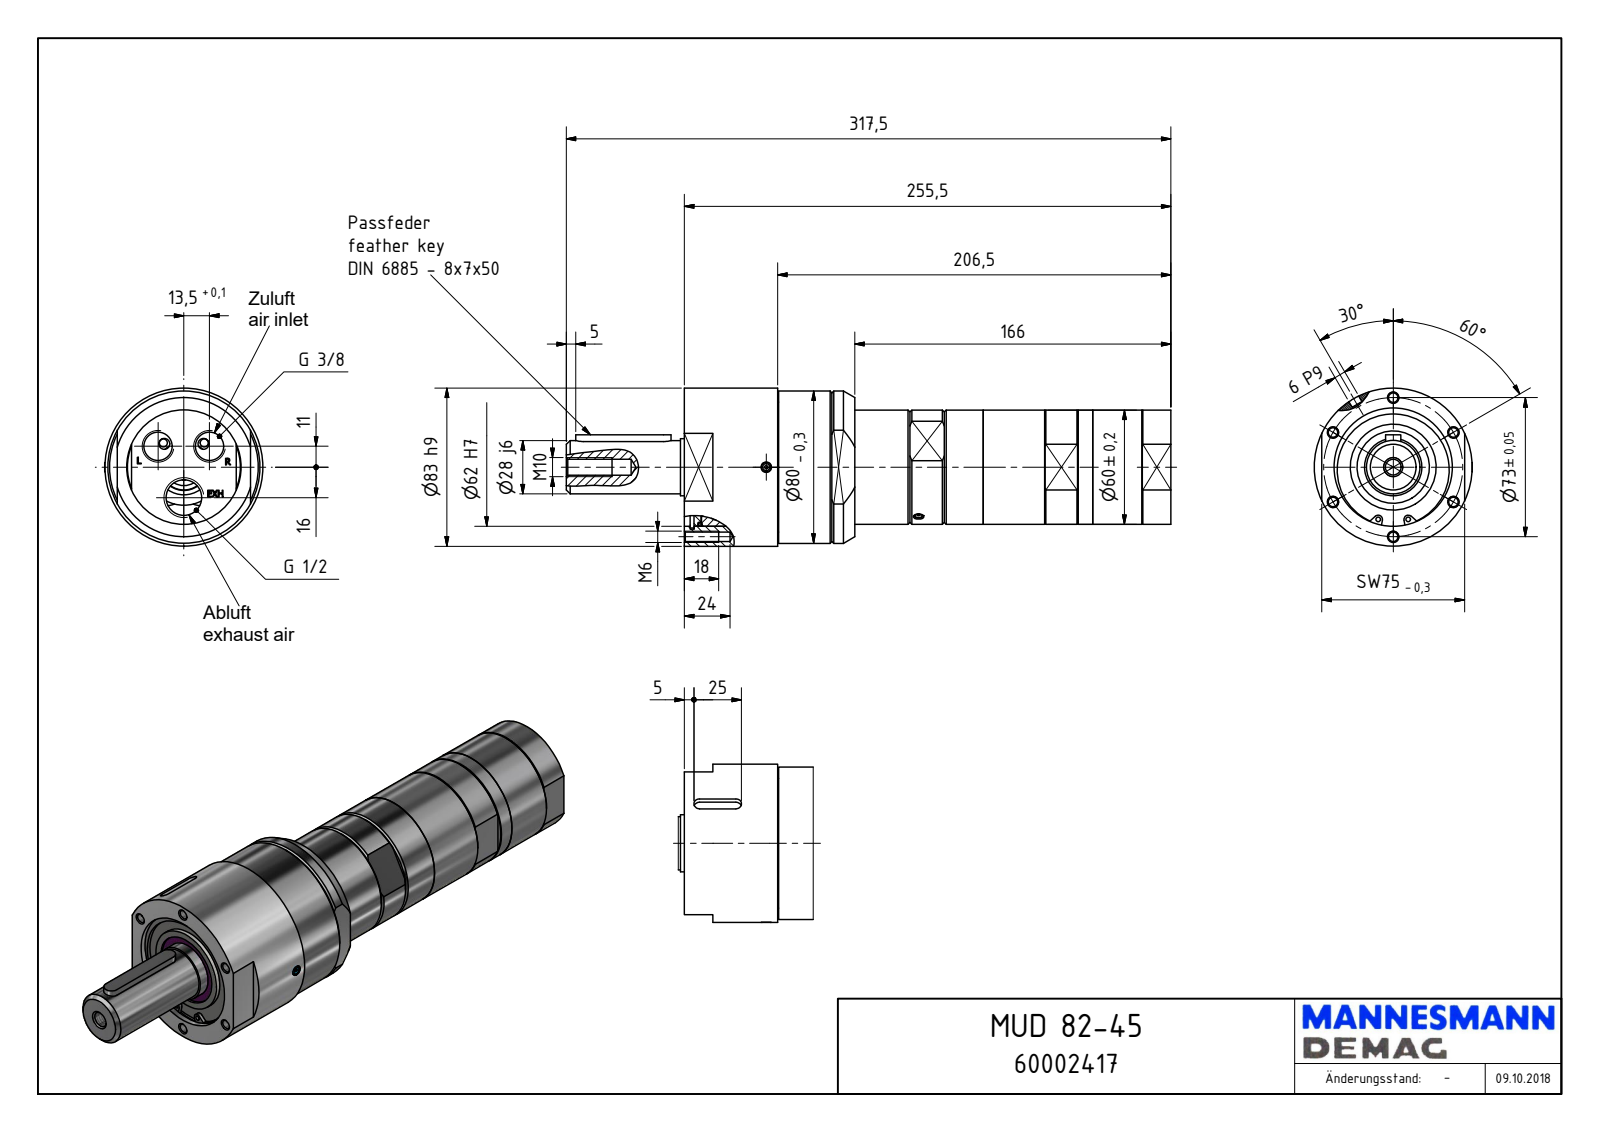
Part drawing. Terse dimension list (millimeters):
name: MUD 82-45_60002417
written by: Autodesk Inventor 2018 (AUTOMOTIVE_DESIGN)
unit: mm
bodies: 1 solid, 277 faces (141 planar, 76 cylindrical, 60 other)
size: 317.5 × 83 × 83
volume: 936 147 mm³; area: 85 691 mm²
holes: 6× ⌀4.92, 2× ⌀1.55, 2× ⌀2.5, 2× ⌀4, 2× ⌀5.5, 2× ⌀14.95, 1× ⌀8.38, 1× ⌀18.63, 1× ⌀38, 1× ⌀40, 1× ⌀58.69, 1× ⌀62
bosses: 2× ⌀5, 2× ⌀3.6, 1× ⌀83, 1× ⌀80, 1× ⌀68.18, 1× ⌀60, 1× ⌀45, 1× ⌀30
rounds: 2× R2.25, 2× R3, 2× R4, 2× R7.5, 1× R8.5, 1× R19.27, 1× R23.5, 1× R25.1
face distances: 255.5, 49, 206.5, 2.5, 0.5, 5, 65, 44, 250.5, 89.5
hole spacings: 36.5, 63.22, 73, 12.08, 13.81, 17.41, 18.42, 19.51
